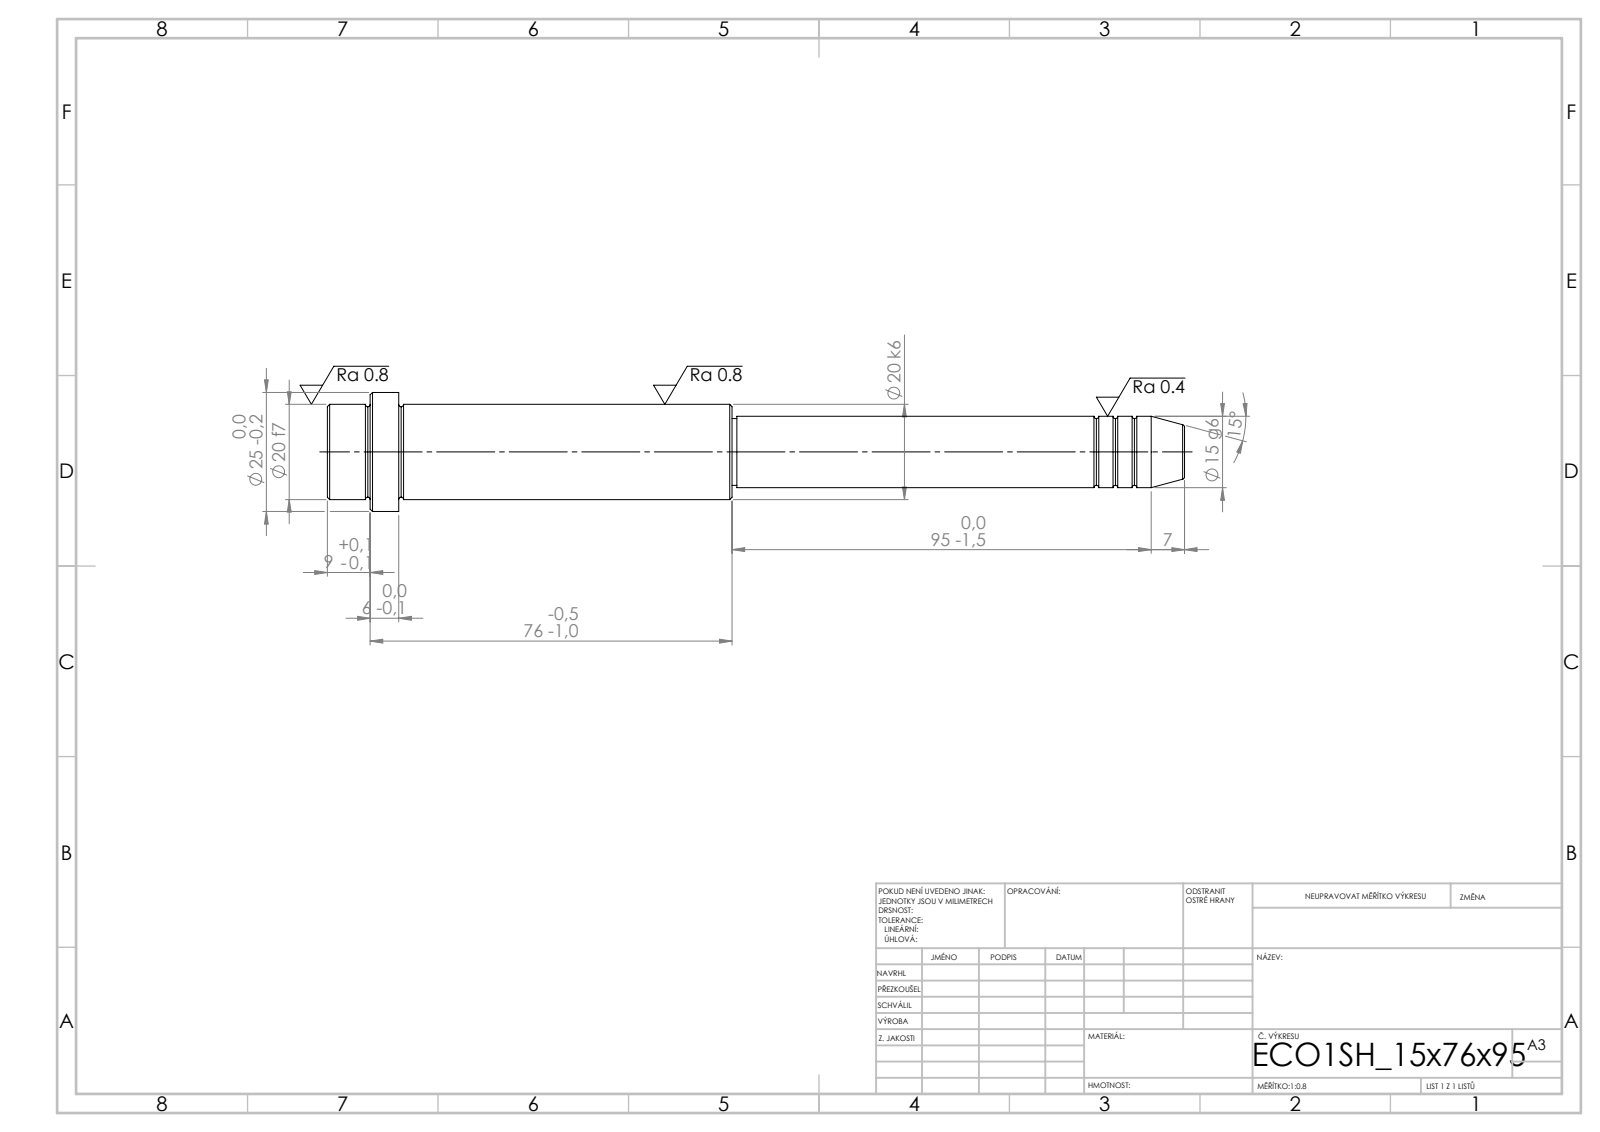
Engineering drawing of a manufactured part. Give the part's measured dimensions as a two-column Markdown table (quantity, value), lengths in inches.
| quantity | value |
| --- | --- |
| STEP written by | SolidWorks 2019 (CONFIG_CONTROL_DESIGN) |
| units | inches |
| bodies | 1 solid, 52 faces (6 planar, 16 cylindrical, 30 other) |
| overall size | 7.087 × 0.984 × 0.984 |
| volume | 2.692 in³ |
| surface area | 16.89 in² |
| round bosses / shafts (diameter × count) | 0.984 × 1, 0.787 × 1, 0.591 × 1, 0.551 × 1 |
| main face-to-face distances | 0.591, 0.236, 0.354, 2.756, 2.992, 3.346, 3.74, 6.496, 6.732, 7.087 |
